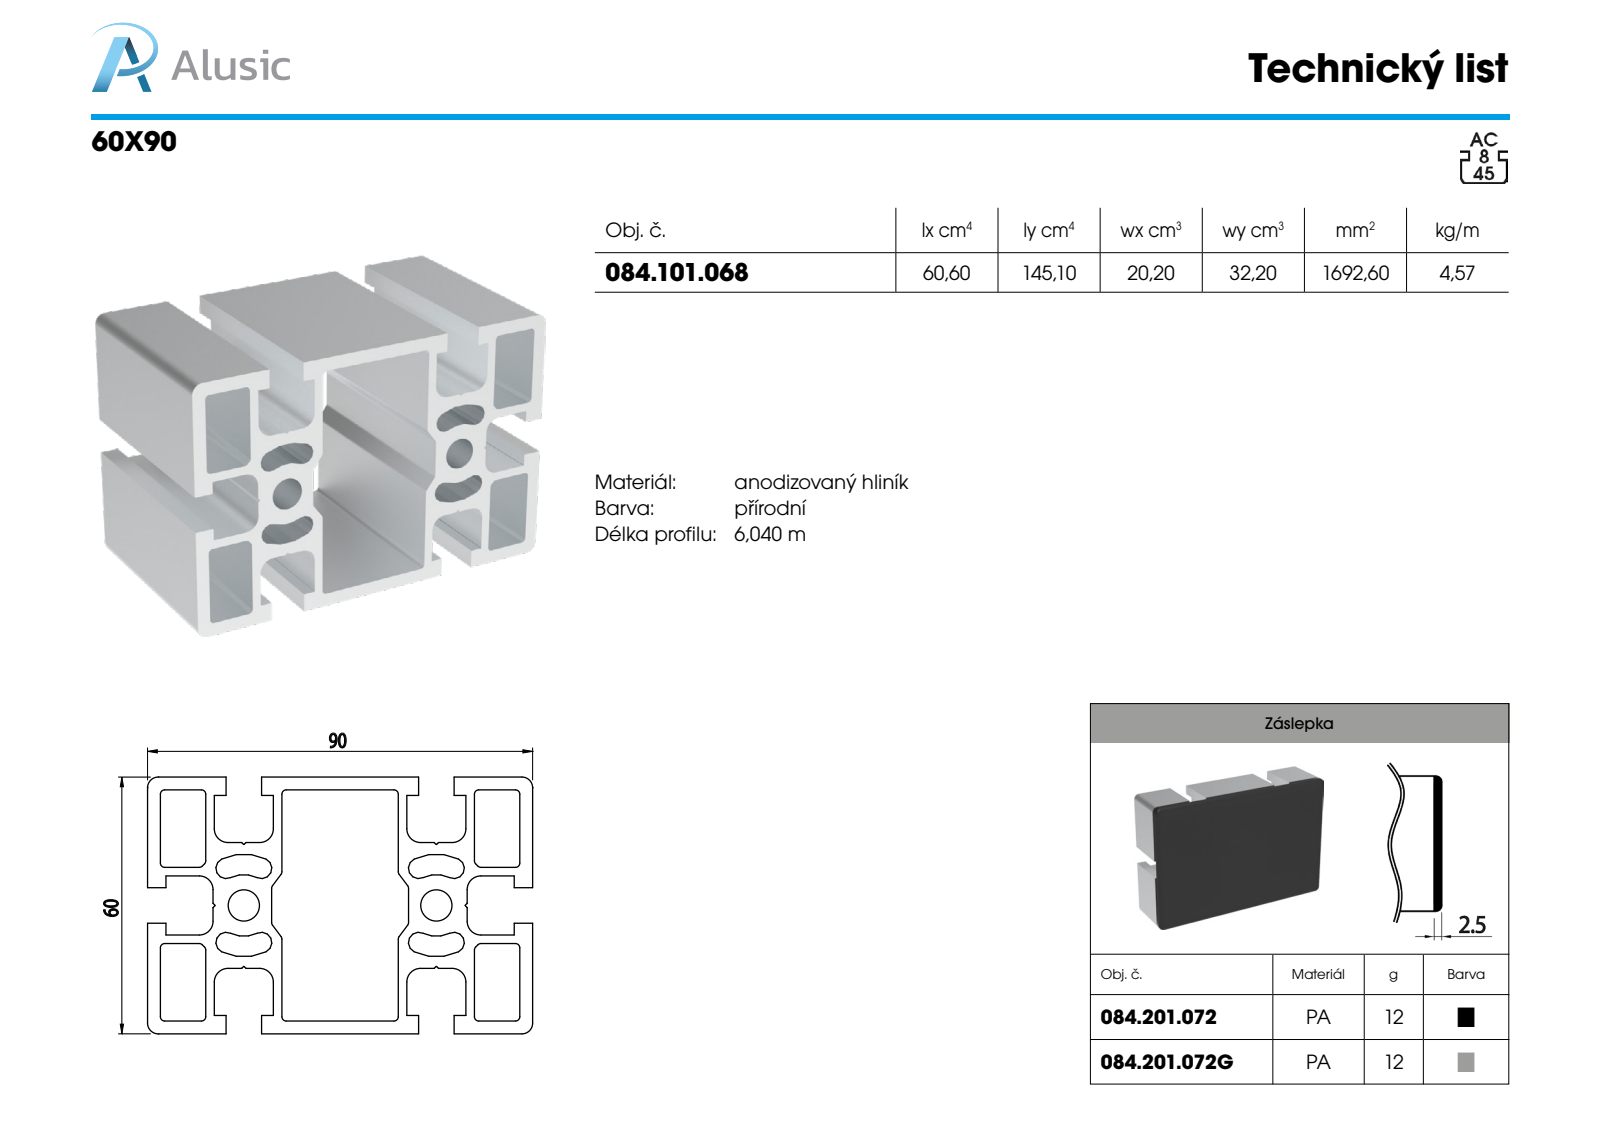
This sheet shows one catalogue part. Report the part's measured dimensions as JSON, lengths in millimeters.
{"part_name": "084.101.068", "step_written_by": "SolidWorks 2018 (AUTOMOTIVE_DESIGN)", "units": "millimeters", "bodies": {"solids": 1, "faces": 247, "planar": 176, "cylindrical": 71, "other": 0}, "overall_size": [100, 90, 60], "volume_mm3": 169258, "surface_area_mm2": 112381, "round_holes": [[7.3, 2]], "partial_cylinders_radius": [[1, 32], [0.1, 18], [3.2, 12], [2.5, 4]], "face_to_face_distances": [3, 45, 57, 2, 15.8, 31.4, 58.6, 60, 87, 28.4], "hole_center_spacings": [45]}
